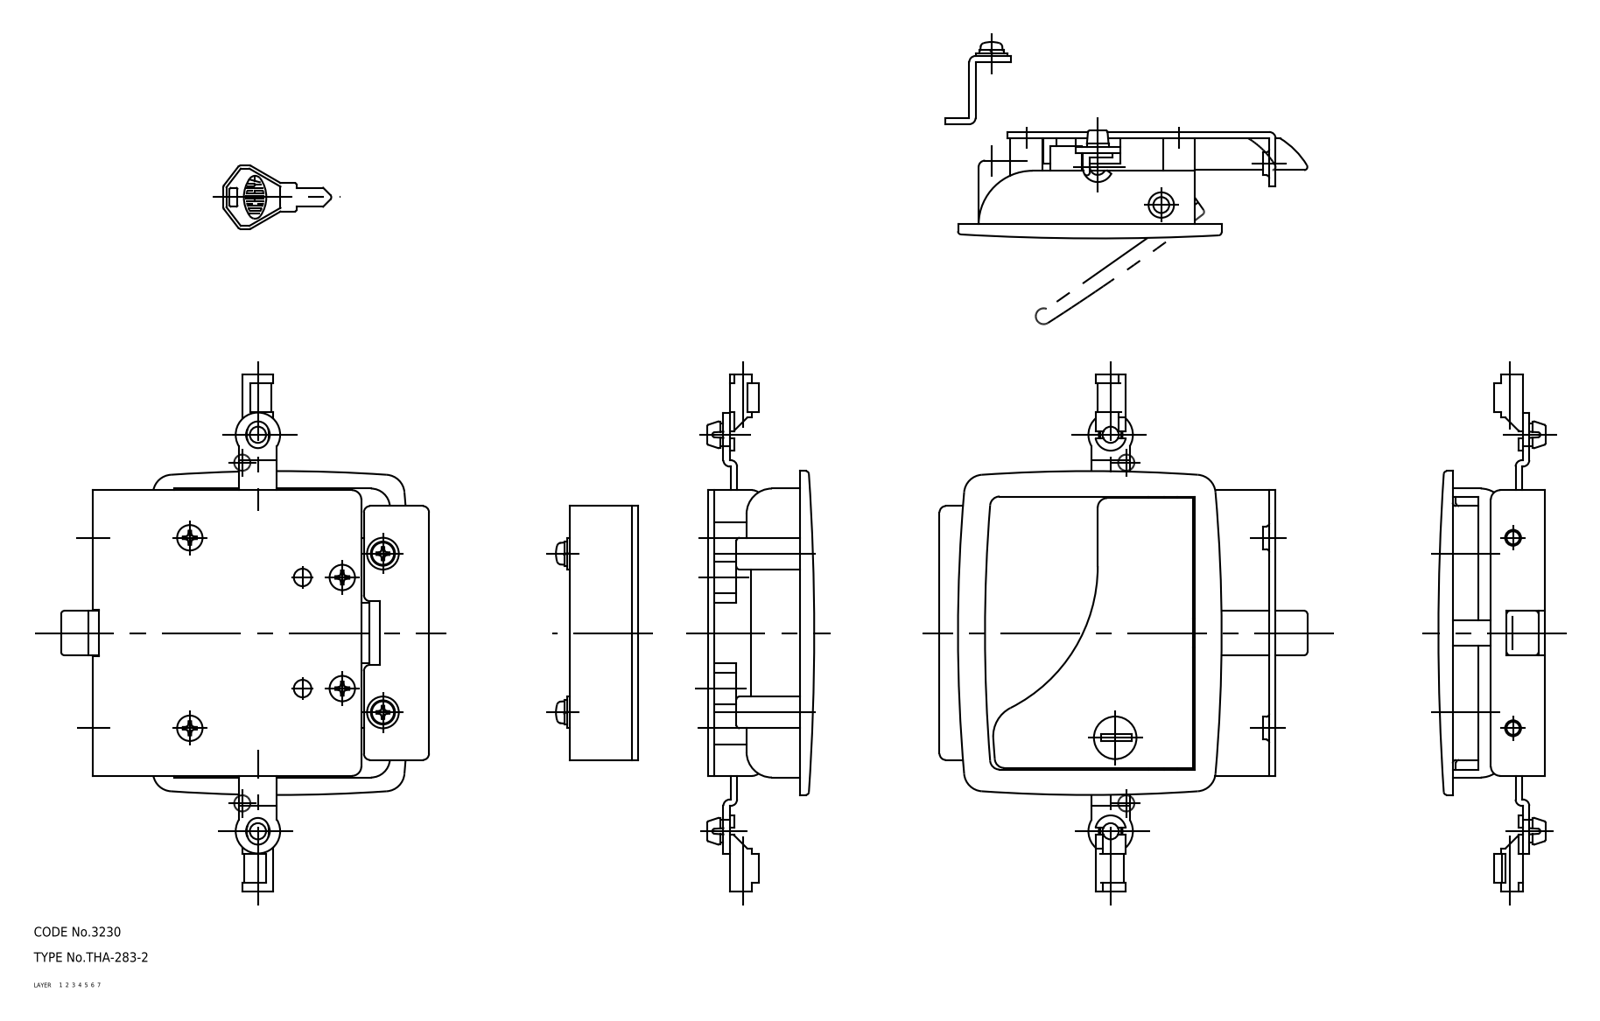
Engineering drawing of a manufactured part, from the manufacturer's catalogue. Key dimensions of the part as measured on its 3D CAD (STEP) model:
Part name (STEP PRODUCT): bracket_B_mr; lock_mr; handle_mr; holder_mr-1 (+8 more)
STEP written by: CADfix (AUTOMOTIVE_DESIGN)
Units: millimetres
Bodies: 15 solids, 807 faces (0 planar, 0 cylindrical, 807 other)
Overall size (bounding box): 163 × 114.5 × 95.99
Volume: 99 599 mm³ · Surface area: 81 089 mm²
